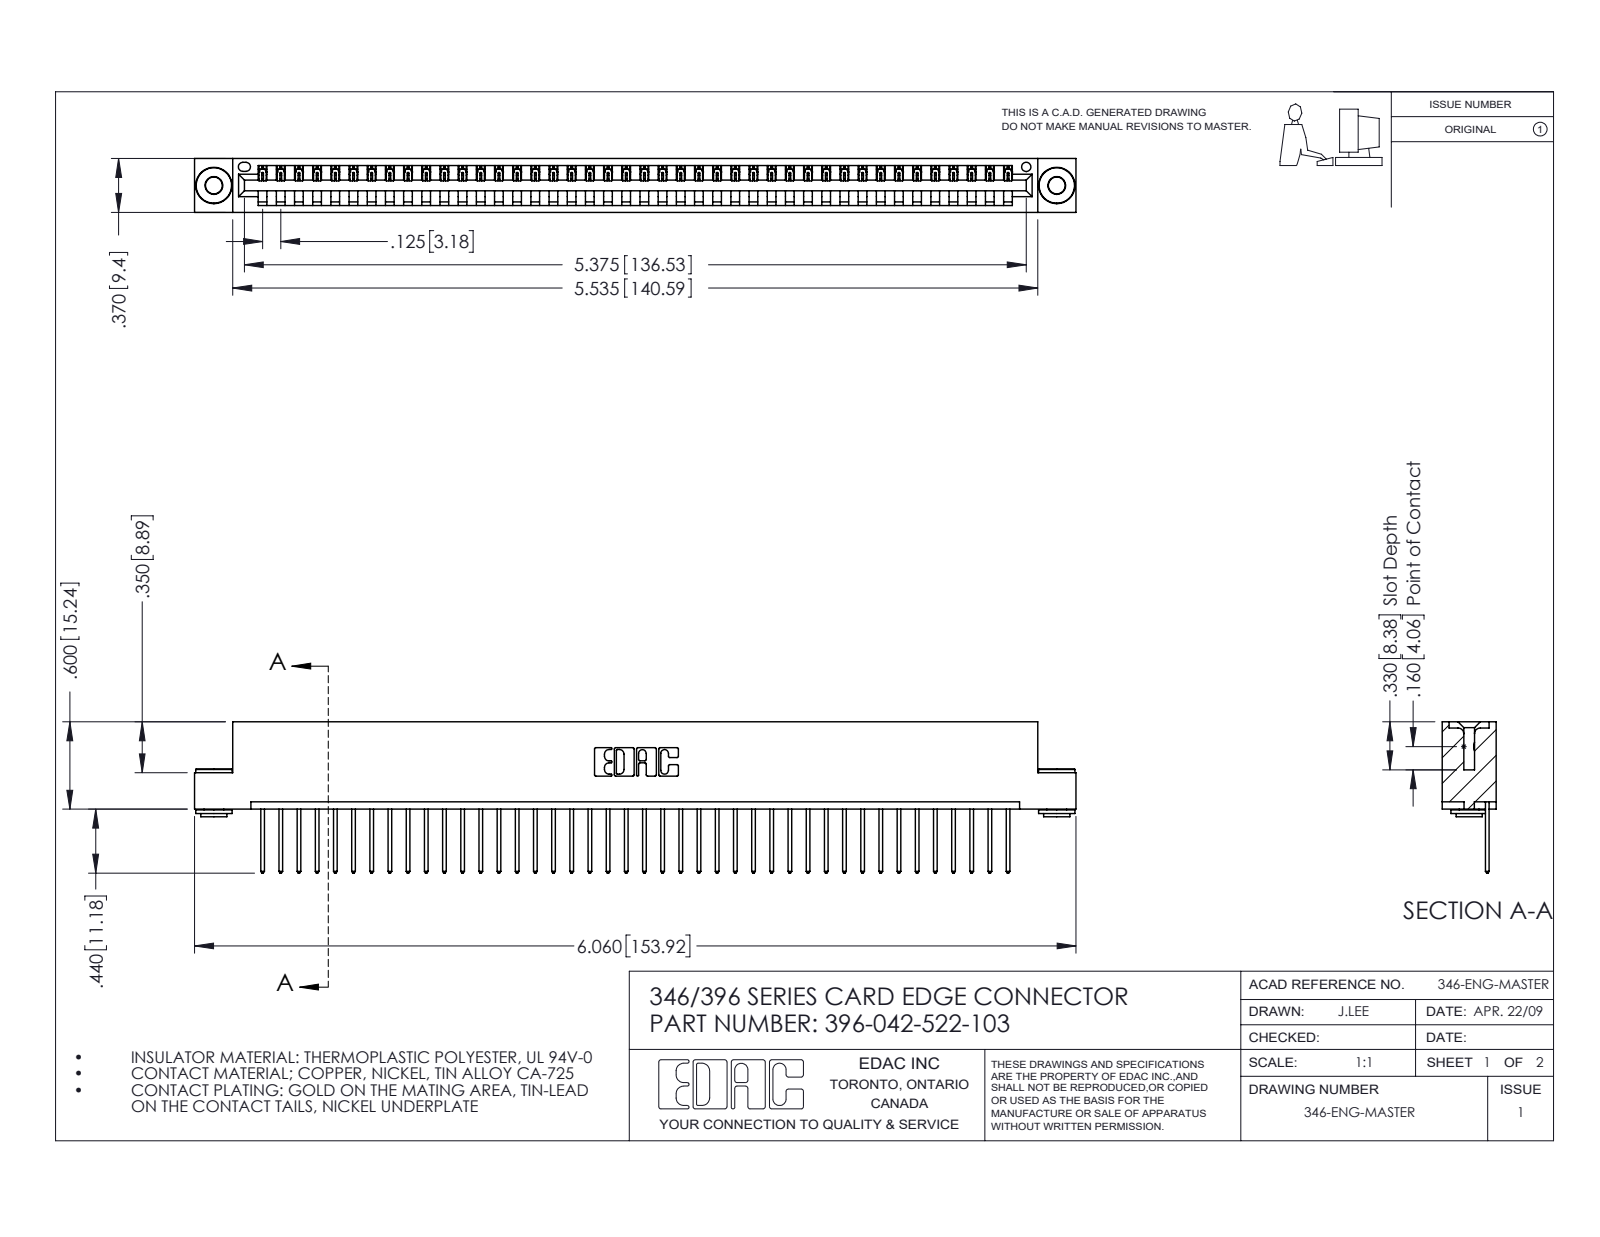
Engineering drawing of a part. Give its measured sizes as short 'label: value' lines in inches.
name: 396-042-522-103; 346 Part_Flush Mounting Lugs - 0.156 Dia-TH; 345-250-002_345-250-002-102; 345-292-001_345-293-122
written by: SolidWorks 2016 (CONFIG_CONTROL_DESIGN)
unit: in
bodies: 45 solids, 2596 faces (1766 planar, 822 cylindrical, 8 other)
size: 6.06 × 1.04 × 0.37
volume: 0.901 in³; area: 29.17 in²
holes: 2× ⌀0.116, 2× ⌀0.156, 1× ⌀0.064
bosses: 2× ⌀0.25, 2× ⌀0.18, 2× ⌀0.136
rounds: 84× R0.006, 84× R0.01, 22× R0.01, 6× R0.007, 6× R0.031, 3× R0.026, 2× R0.031, 2× R0.04
face distances: 0.048, 0.322, 0.37, 0.25, 0.025, 0.072, 0.298, 0.148, 0.222, 0.1
hole spacings: 0.246, 5.586, 5.795
